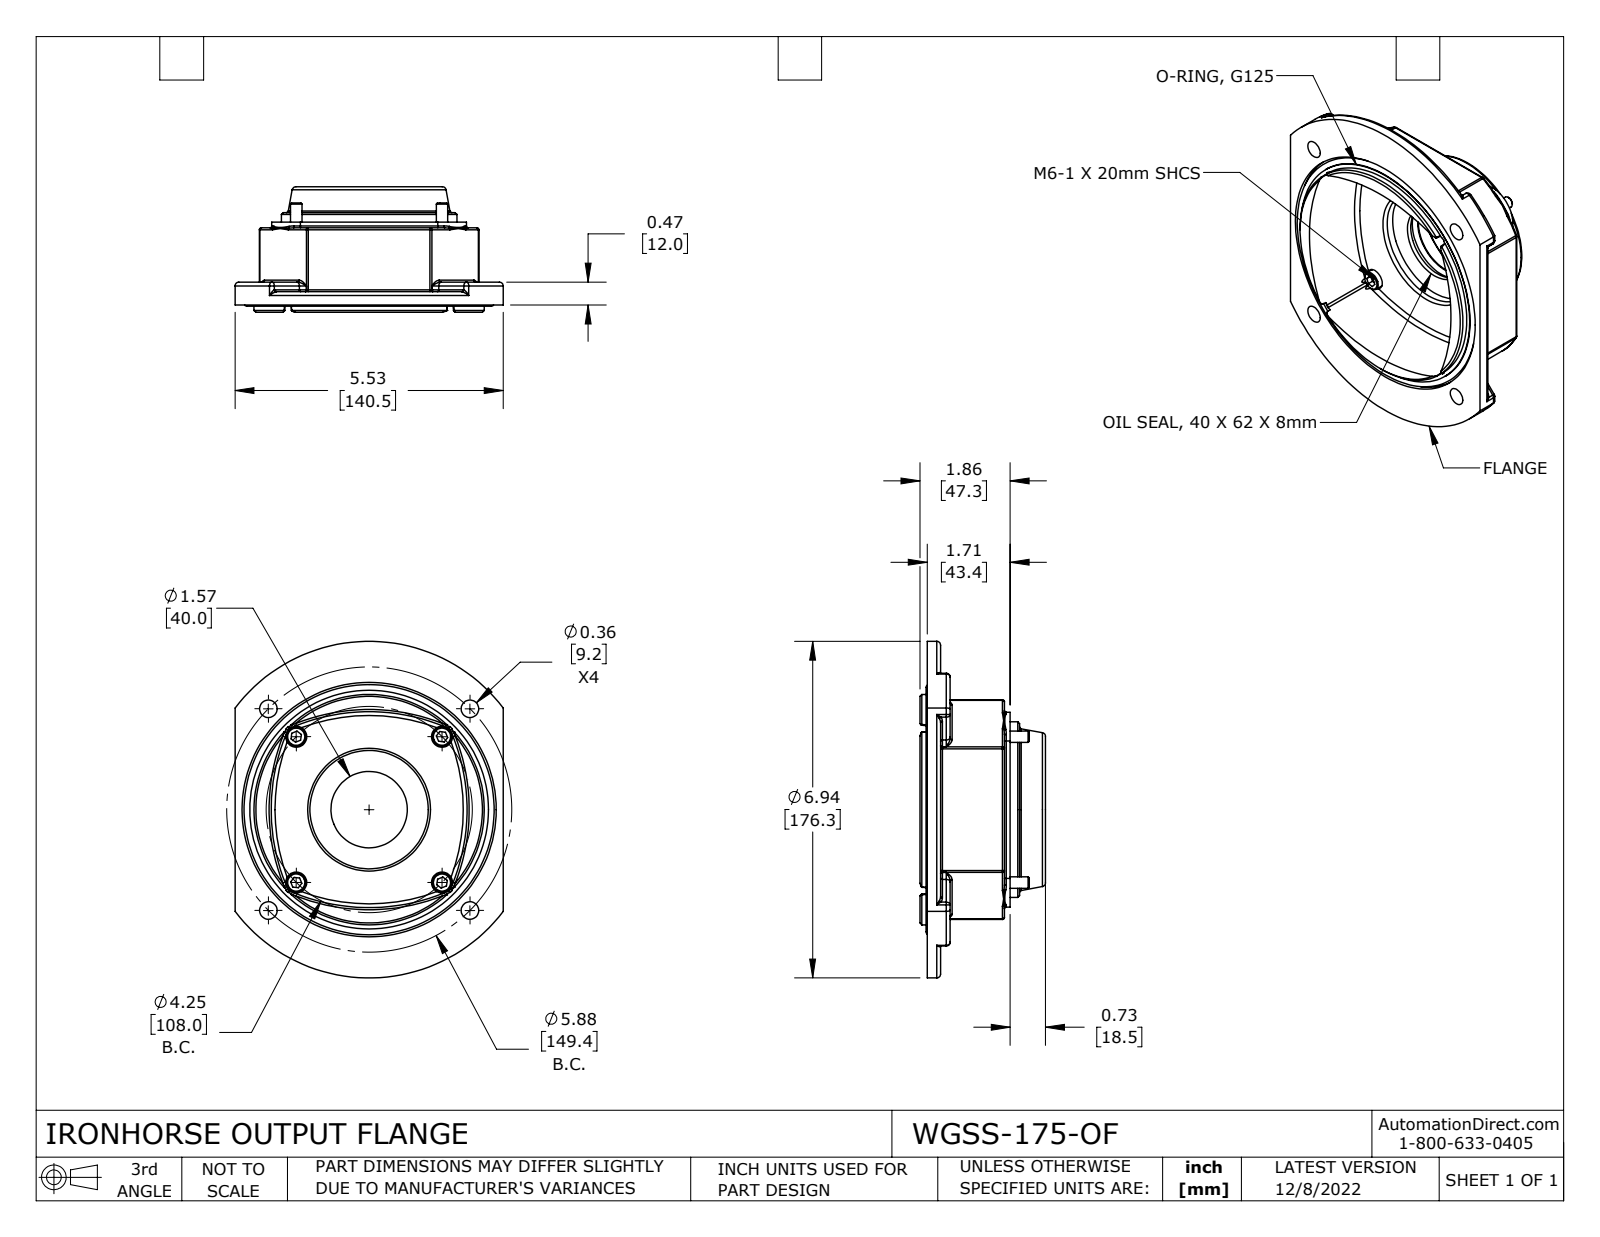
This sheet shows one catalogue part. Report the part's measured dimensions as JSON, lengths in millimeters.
{"part_name": "WGSS-175-OF", "step_written_by": "SolidWorks 2021 (CONFIG_CONTROL_DESIGN)", "units": "millimeters", "bodies": {"solids": 7, "faces": 421, "planar": 95, "cylindrical": 137, "other": 189}, "overall_size": [176.28, 140.46, 65.76], "volume_mm3": 335106, "surface_area_mm2": 97513, "round_holes": [[7, 4], [9.2, 4], [11, 4], [40, 1], [56, 1], [57, 1], [62, 1], [68, 1], [133.2, 1]], "round_bosses_or_shafts": [[10, 4], [6, 4], [125, 1], [120.65, 1], [92, 1], [46, 1]], "partial_cylinders_radius": [[2, 24], [1, 20], [3, 8], [15, 4], [66, 1], [88.14, 1]], "face_to_face_distances": [7, 36.45, 23.45, 30.45, 115, 4, 13, 43.45, 3, 5], "hole_center_spacings": [92.15, 20.68, 53.99, 74.67, 76.36, 105.6, 128.67, 107.99]}
